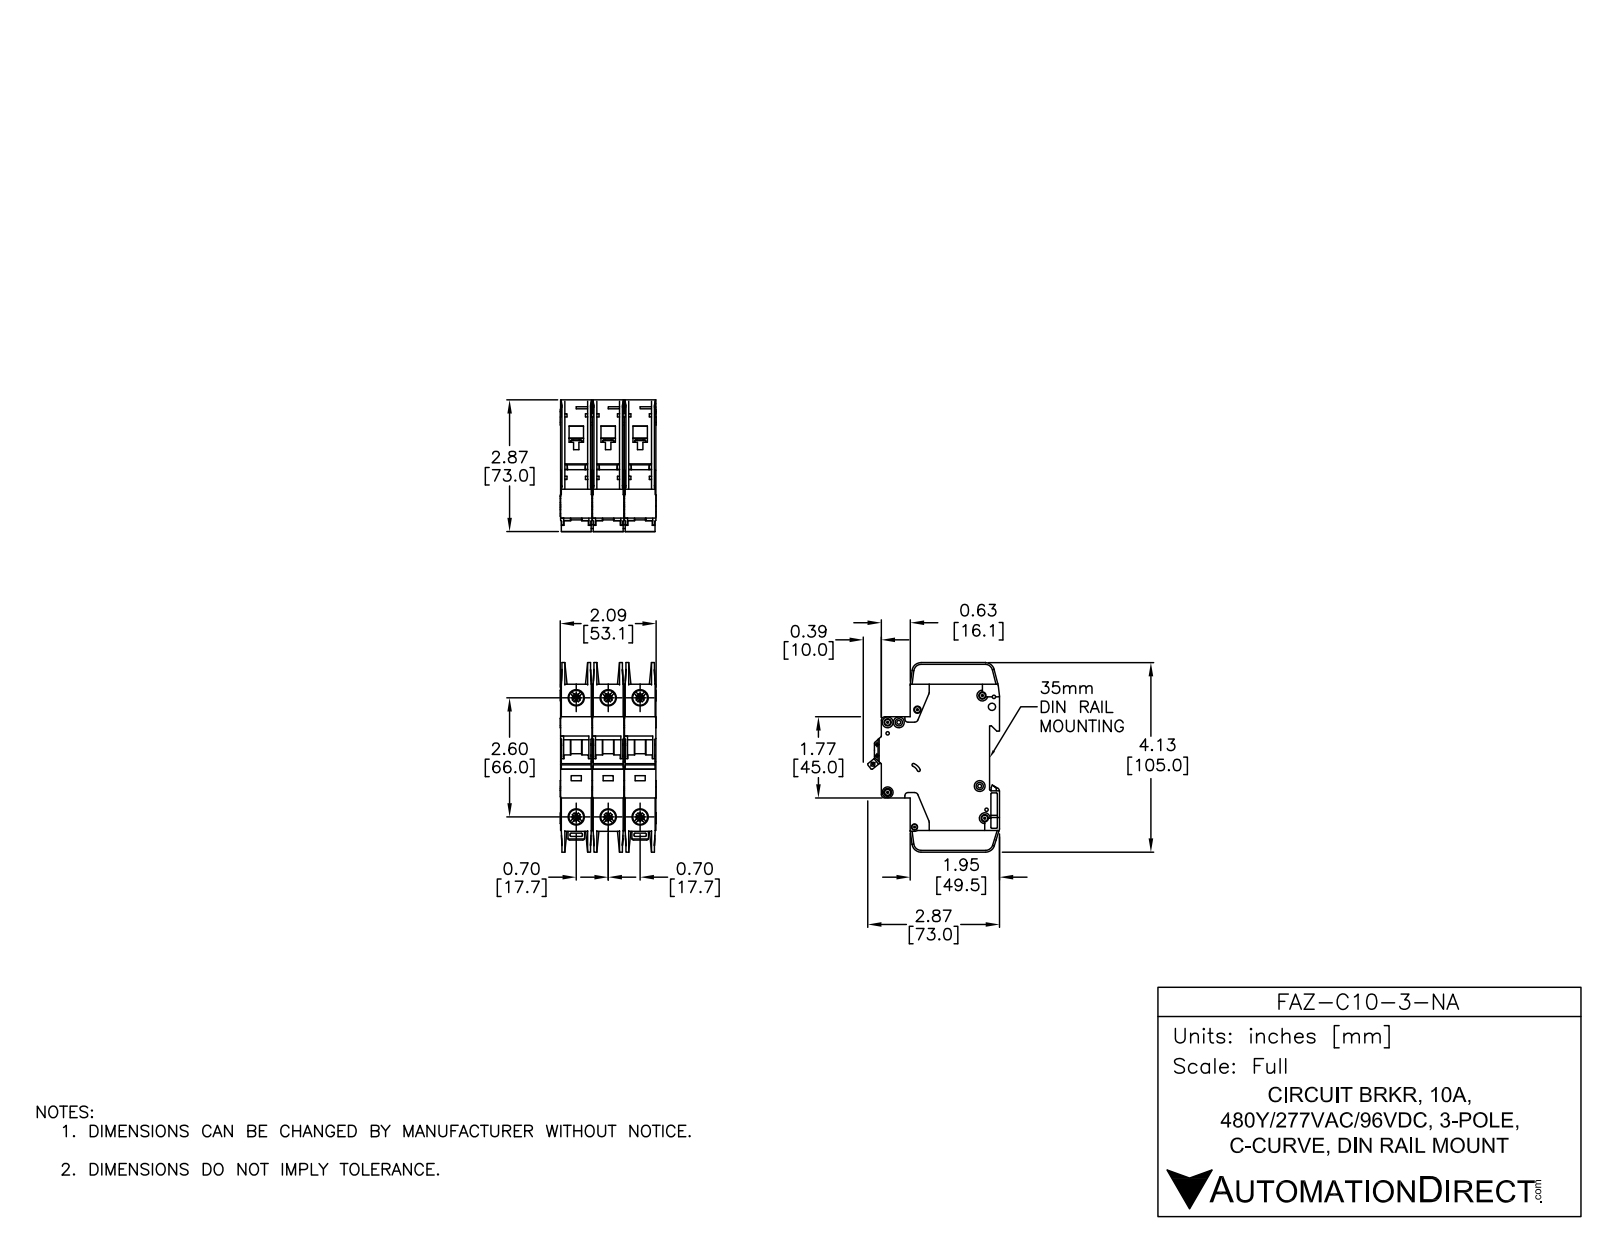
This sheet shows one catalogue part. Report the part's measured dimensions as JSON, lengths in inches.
{"part_name": "FAZ-C10-3-NA", "step_written_by": "SolidWorks 2014 (AUTOMOTIVE_DESIGN)", "units": "inches", "bodies": {"solids": 9, "faces": 2352, "planar": 1227, "cylindrical": 789, "other": 336}, "overall_size": [4.134, 2.876, 2.091], "volume_in3": 14.22, "surface_area_in2": 115, "round_holes": [[0.142, 7], [0.281, 6], [0.323, 6], [0.043, 2], [0.059, 2], [0.157, 2], [0.075, 1], [0.085, 1], [0.087, 1], [0.1, 1], [0.13, 1], [0.134, 1]], "round_bosses_or_shafts": [[0.236, 7], [0.098, 3]], "partial_cylinders_radius": [[0.01, 65], [0.02, 30], [0.039, 26], [0.079, 14], [0.071, 5], [0.197, 5], [0.157, 4], [0.008, 2]], "face_to_face_distances": [0.697, 1.394, 0.689, 1.386, 0.028, 0.593, 0.096, 0.069, 0.62, 0.524], "hole_center_spacings": [0.697, 2.69, 2.598, 0.244, 1.394, 2.948, 0.204, 0.24]}
